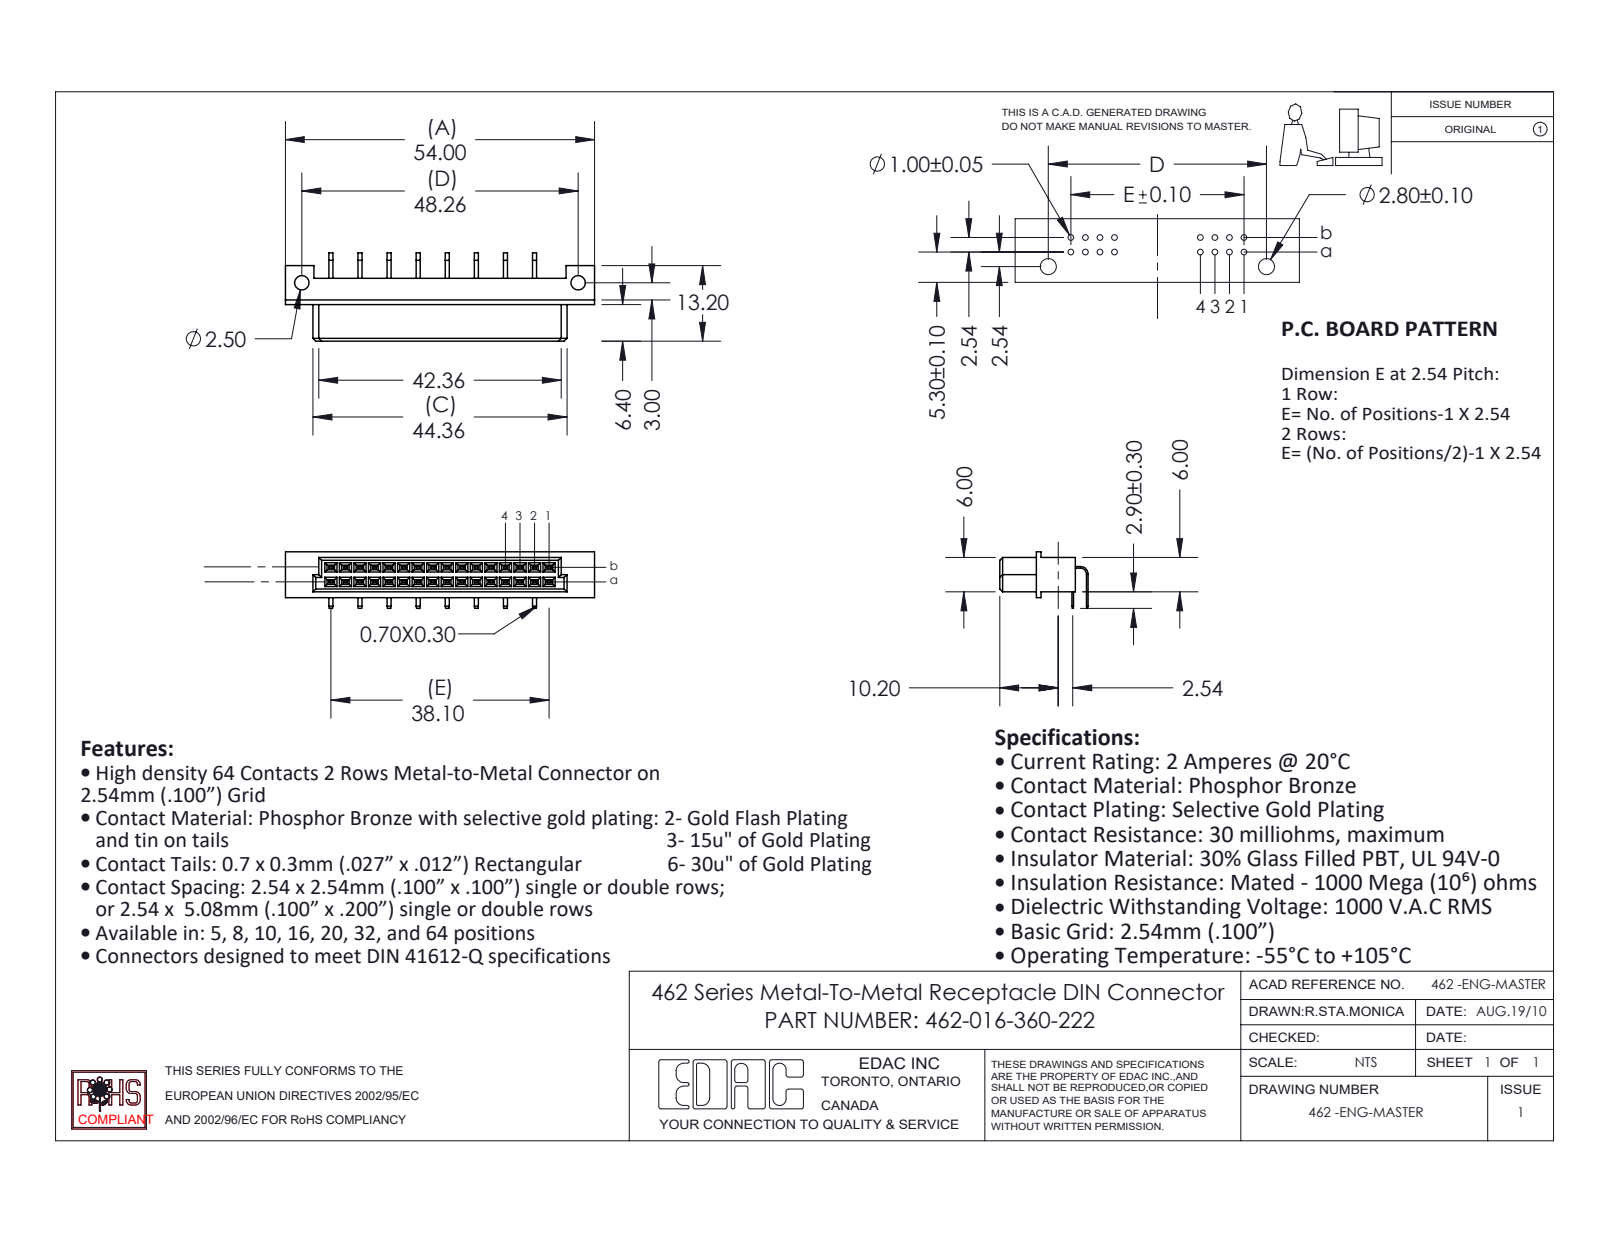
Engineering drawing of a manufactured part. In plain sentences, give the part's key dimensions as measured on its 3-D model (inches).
The part is named "462-290-1; 462-016-360-222; 462 Part_32; 462-290-2". Its 3-D file was written by "SolidWorks 2020 (CONFIG_CONTROL_DESIGN)". It is 17 solids with 675 faces: 639 planar, 36 cylindrical and 0 other. Overall it measures 2.126 by 0.607 by 0.39 inches. Its volume is 0.188 cubic inches and its surface area 5.74 square inches. Round holes: 2 of diameter 0.098. Partial cylindrical surfaces (rounded edges, fillets, slot ends): 2 of radius 0.04, 2 of radius 0.052. The main face-to-face distances are 0.236, 0.1, 0.032, 0.181, 0.062, 0.074, 0.162, 0.174, 0.022, 0.022. The hole center spacings are 1.9.
